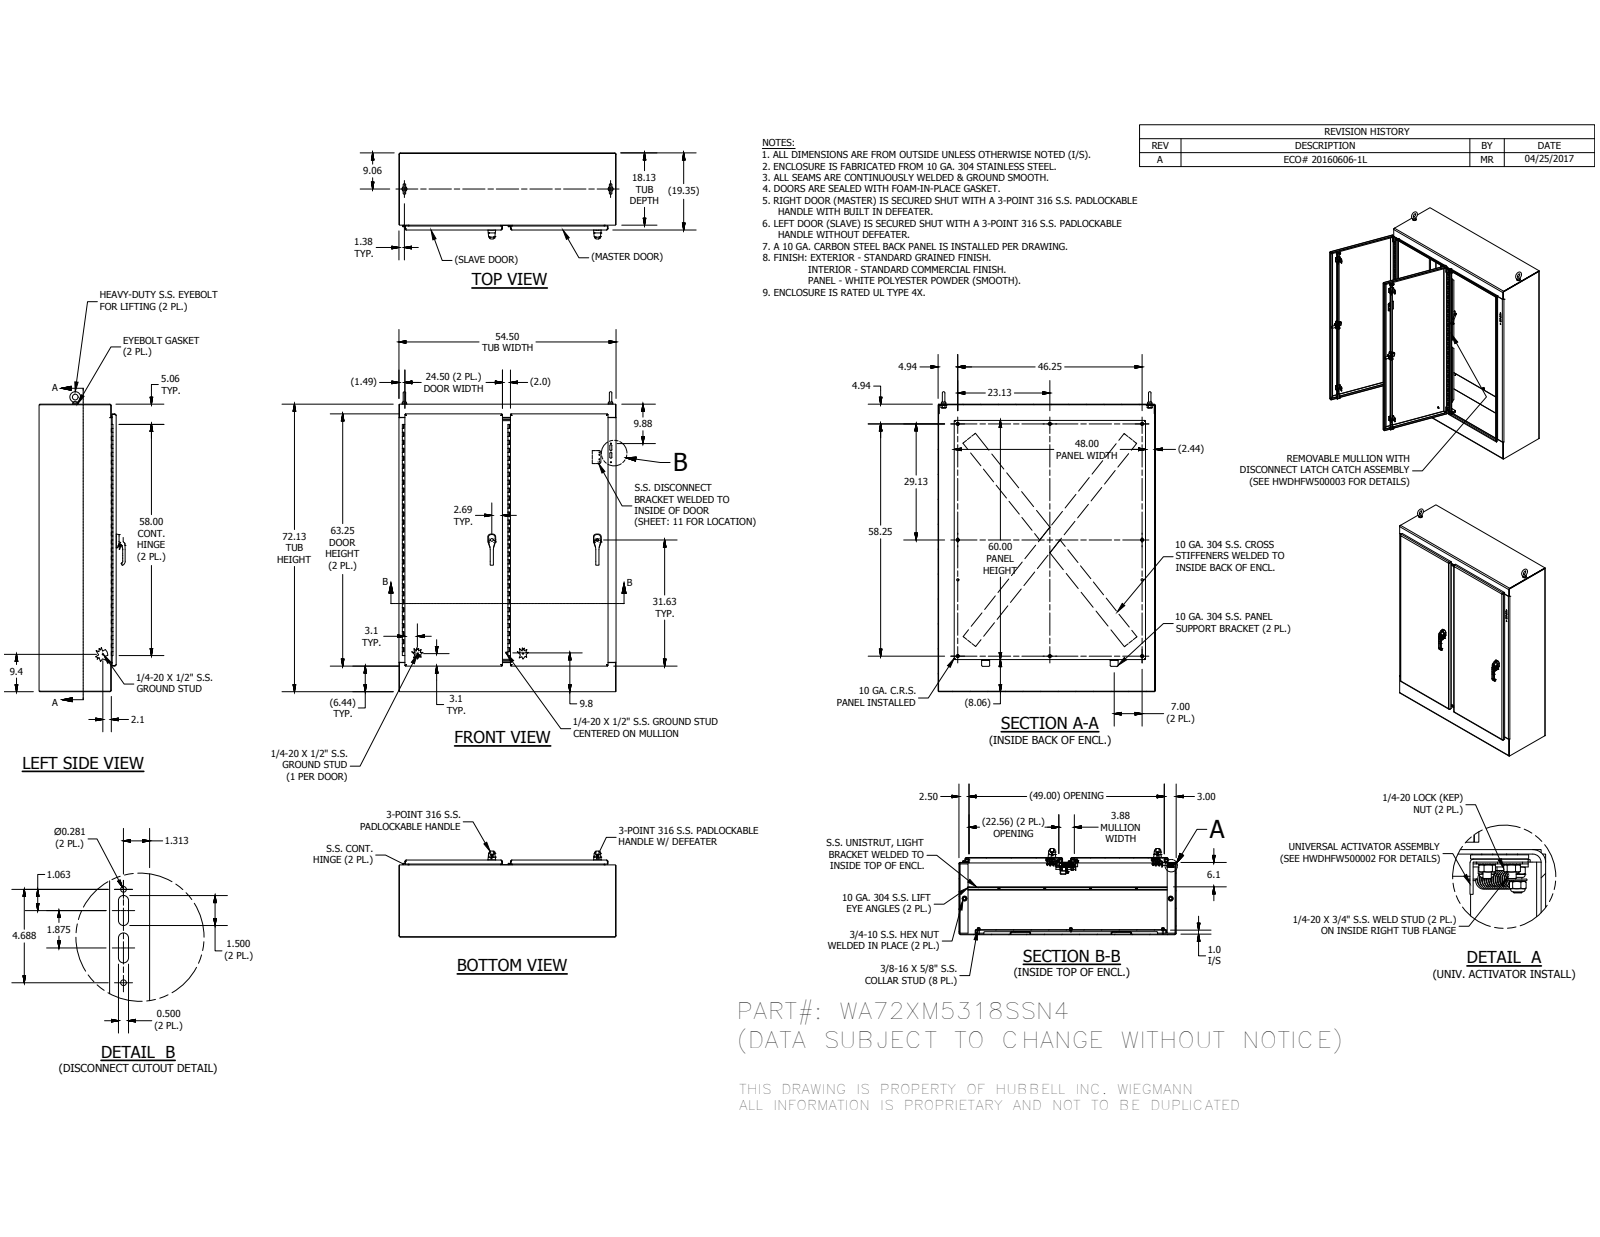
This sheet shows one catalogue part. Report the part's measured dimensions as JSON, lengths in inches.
{"part_name": "WA72XM5318SSN4BLR; WAXM5318SSN4TOP; WAXM5318SSN4BTM; HFW332010S (+8 more)", "step_written_by": "Autodesk Inventor 2016 (AUTOMOTIVE_DESIGN)", "units": "inches", "bodies": {"solids": 255, "faces": 10678, "planar": 5046, "cylindrical": 3504, "other": 2128}, "overall_size": [75.248, 54.5, 21.599], "volume_in3": 2526, "surface_area_in2": 37820, "round_holes": [[0.14, 48], [0.375, 18], [0.25, 17], [0.563, 10], [0.187, 9], [0.136, 8], [0.164, 8], [0.19, 8], [0.196, 8], [0.201, 8], [0.262, 8], [0.289, 8]], "round_bosses_or_shafts": [[0.33, 18], [0.25, 18], [0.625, 13], [0.337, 12], [0.375, 11], [0.563, 9], [0.28, 8], [0.237, 8]], "partial_cylinders_radius": [[0.02, 359], [0.012, 222], [0.02, 192], [0.125, 47], [0.019, 42], [0.063, 36], [0.25, 33], [0.05, 28]], "face_to_face_distances": [0.134, 19.217, 0.134, 19.083, 1, 19.35, 1.134, 18.217, 1.268, 1.134], "hole_center_spacings": [0.018, 26.383, 26.389, 26.38, 26.385, 26.386, 26.391, 54.25]}
